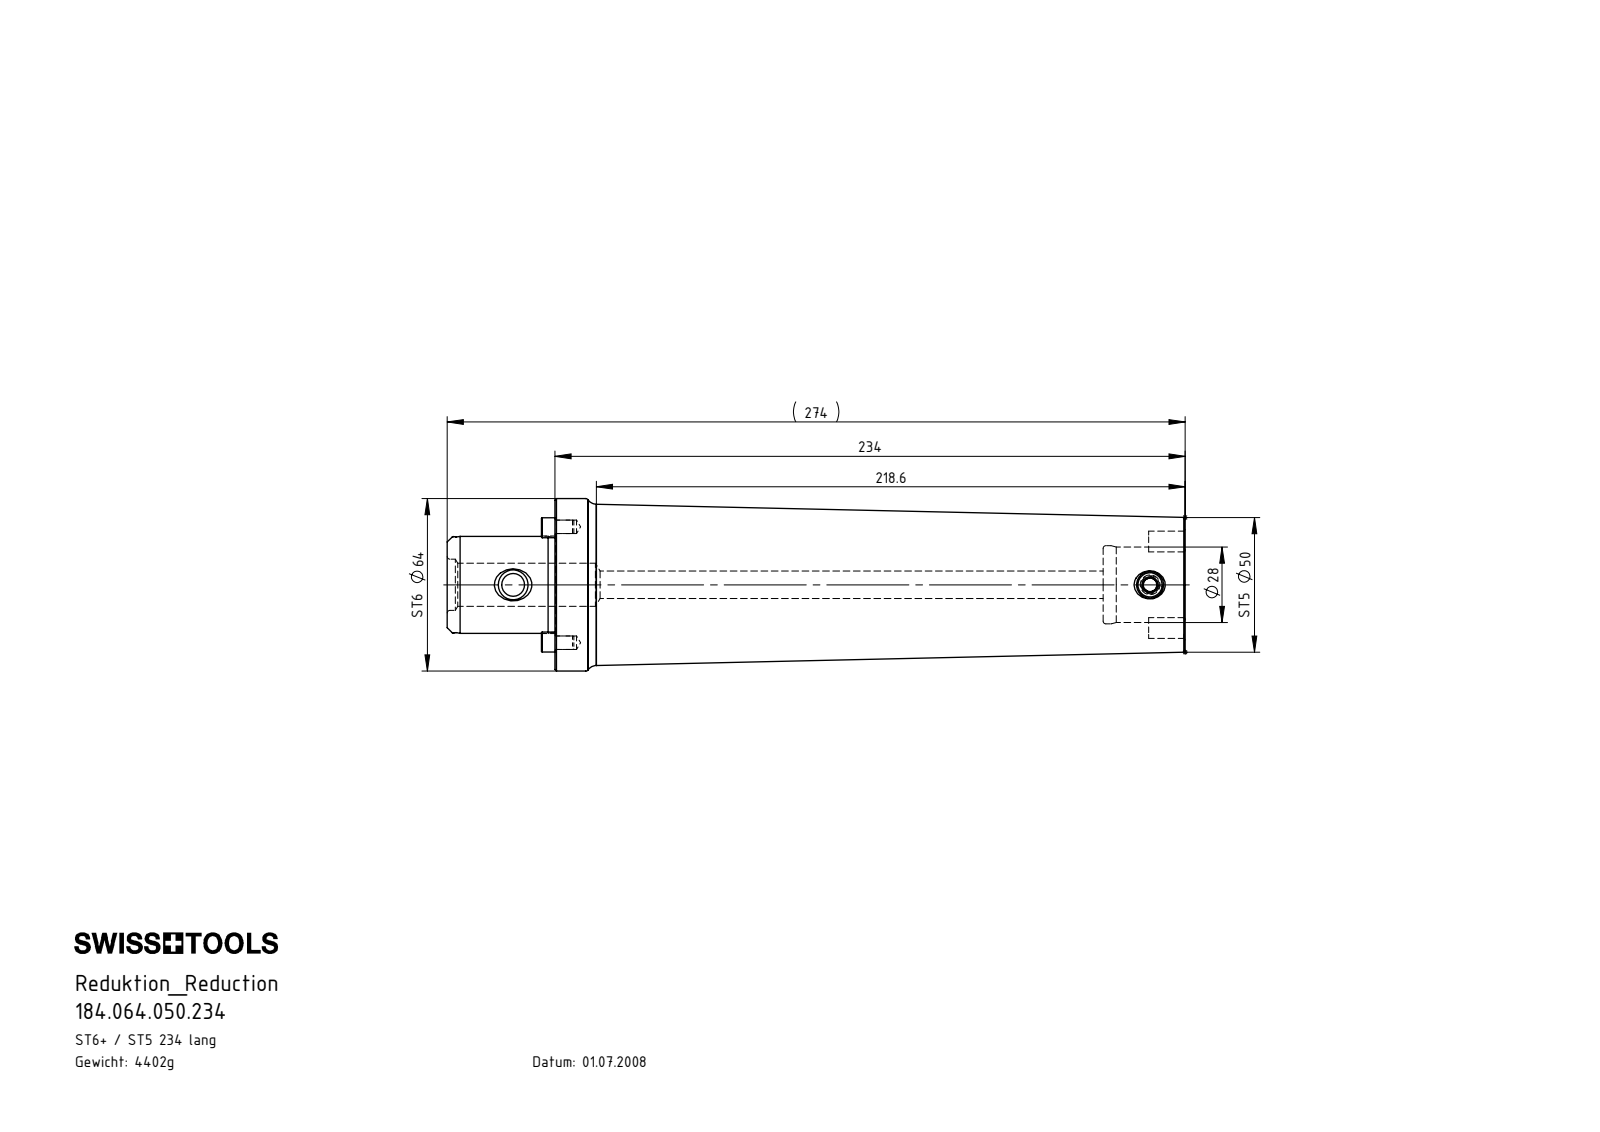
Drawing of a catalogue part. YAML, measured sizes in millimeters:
part_name: "ST6-ER2.001.012_A; ST5-ER1.001.012_A; ST6-ST5.K01.234; ST6-ST5.K01.234_A"
step_written_by: "SolidWorks 2015 (CONFIG_CONTROL_DESIGN)"
units: millimeters
bodies: {solids: 4, faces: 164, planar: 26, cylindrical: 47, other: 91}
overall_size: [274, 64, 64]
volume: 560903
surface_area: 63840
round_holes:
  - {diameter: 5, count: 2}
  - {diameter: 8.5, count: 1}
  - {diameter: 9, count: 1}
  - {diameter: 10.2, count: 1}
  - {diameter: 16, count: 1}
  - {diameter: 19, count: 1}
  - {diameter: 28, count: 1}
  - {diameter: 29, count: 1}
round_bosses_or_shafts:
  - {diameter: 64, count: 1}
  - {diameter: 36, count: 1}
  - {diameter: 35.8, count: 1}
  - {diameter: 35.3, count: 1}
  - {diameter: 10, count: 1}
partial_cylinders:
  - {radius: 0.5, count: 4}
  - {radius: 4.2, count: 2}
  - {radius: 5.47, count: 2}
  - {radius: 18.05, count: 2}
face_to_face_distances: [234, 203.5, 30.5, 40, 243.5, 274, 24.1, 5, 35, 208.5]
hole_center_spacings: [21.5, 43, 236.45]
